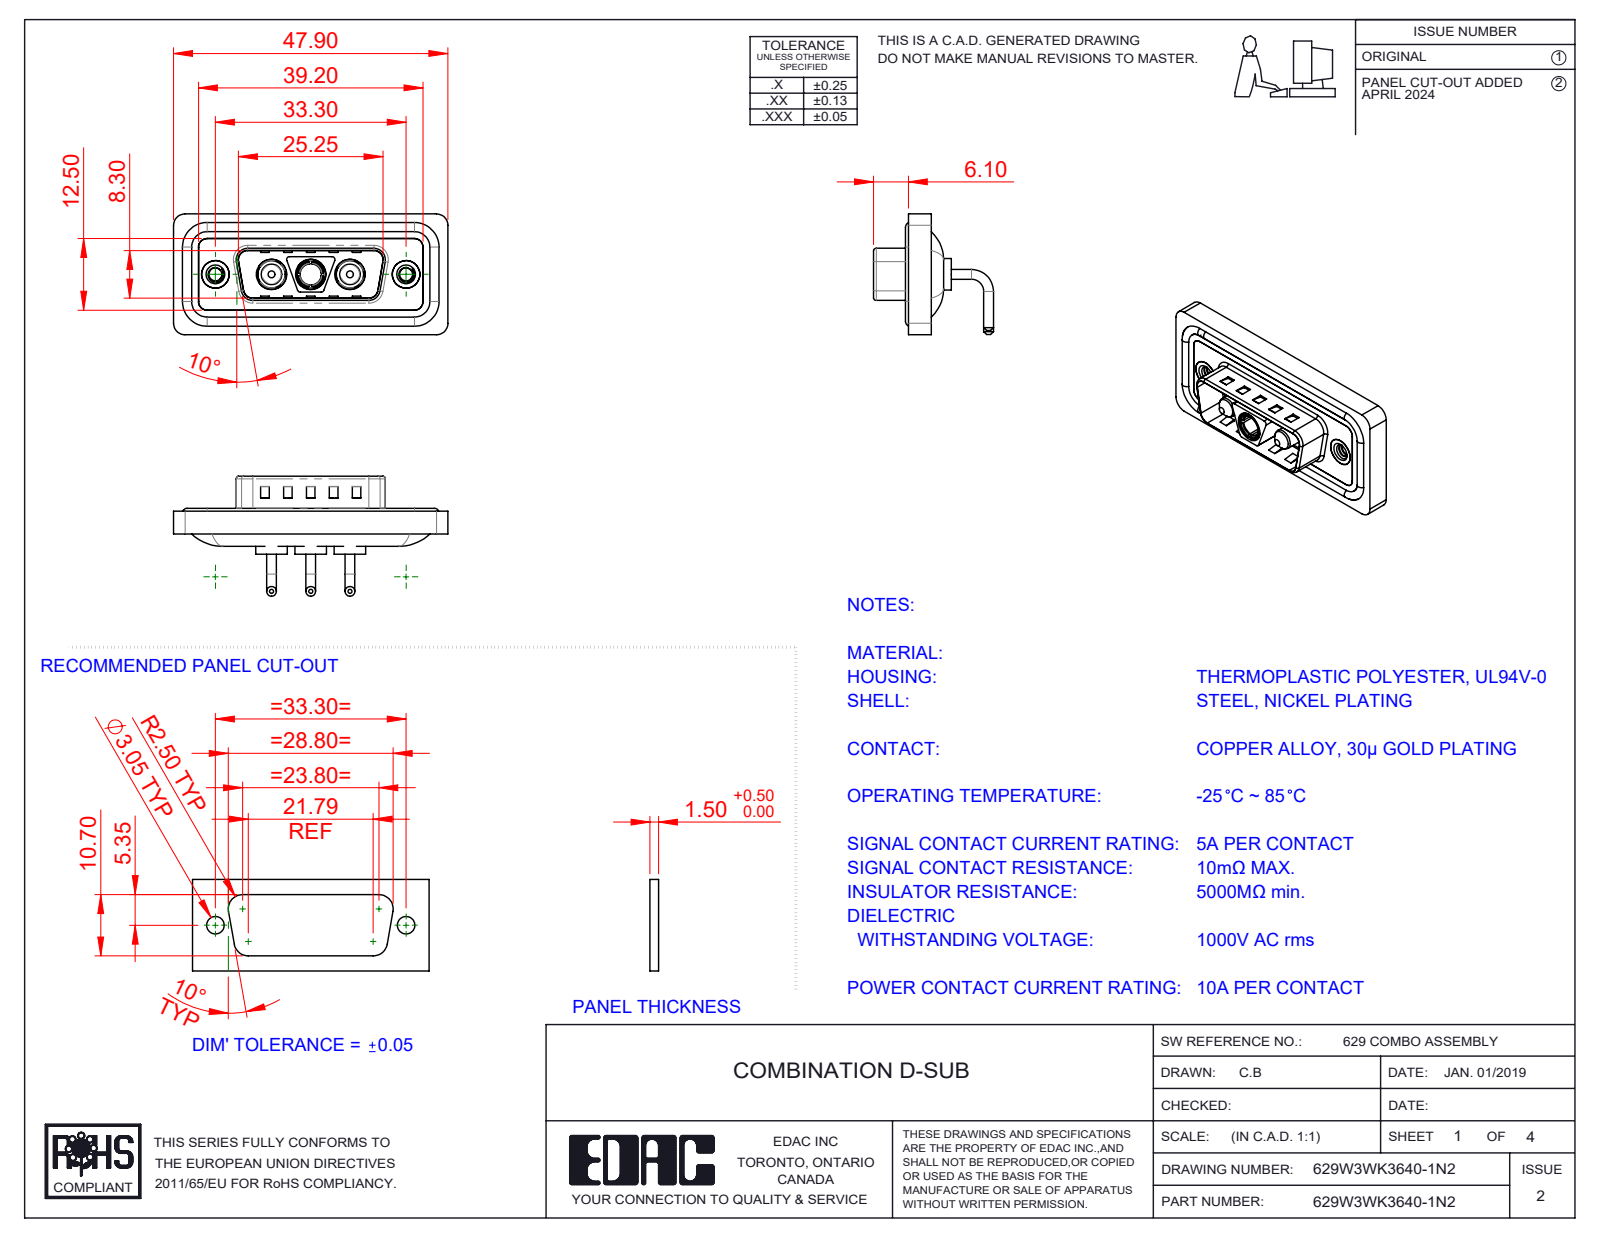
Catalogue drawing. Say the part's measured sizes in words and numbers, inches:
The part is named "629Combo Shell Front_15 Contacts; 629Combo Shell Rear_15 Contacts; 629Combo Housing_3WK3; Power Pin_10A RA (+4 more)". Its 3-D file was written by "SolidWorks 2023 (CONFIG_CONTROL_DESIGN)". It is 13 solids with 621 faces: 231 planar, 256 cylindrical and 134 other. Overall it measures 1.886 by 0.831 by 0.825 inches. Its volume is 0.349 cubic inches and its surface area 14.35 square inches. Round holes: 3 of diameter 0.191, 3 of diameter 0.209, 2 of diameter 0.089, 2 of diameter 0.157, 2 of diameter 0.189, 2 of diameter 0.197, 1 of diameter 0.146. Round bosses or shafts: 6 of diameter 0.067, 4 of diameter 0.063, 3 of diameter 0.217, 3 of diameter 0.205, 3 of diameter 0.187, 3 of diameter 0.148, 2 of diameter 0.193, 2 of diameter 0.142. Partial cylindrical surfaces (rounded edges, fillets, slot ends): 20 of radius 0.079, 18 of radius 0.059, 12 of radius 0.02, 8 of radius 0.063, 4 of radius 0.01, 4 of radius 0.024, 4 of radius 0.026, 4 of radius 0.035. The main face-to-face distances are 0.016, 0.114, 0.031, 0.043, 0.083, 0.063, 0.122, 0.098, 0.177, 0.059. The hole center spacings are 0.27, 0.386, 0.656, 0.925, 0.539, 1.311.
